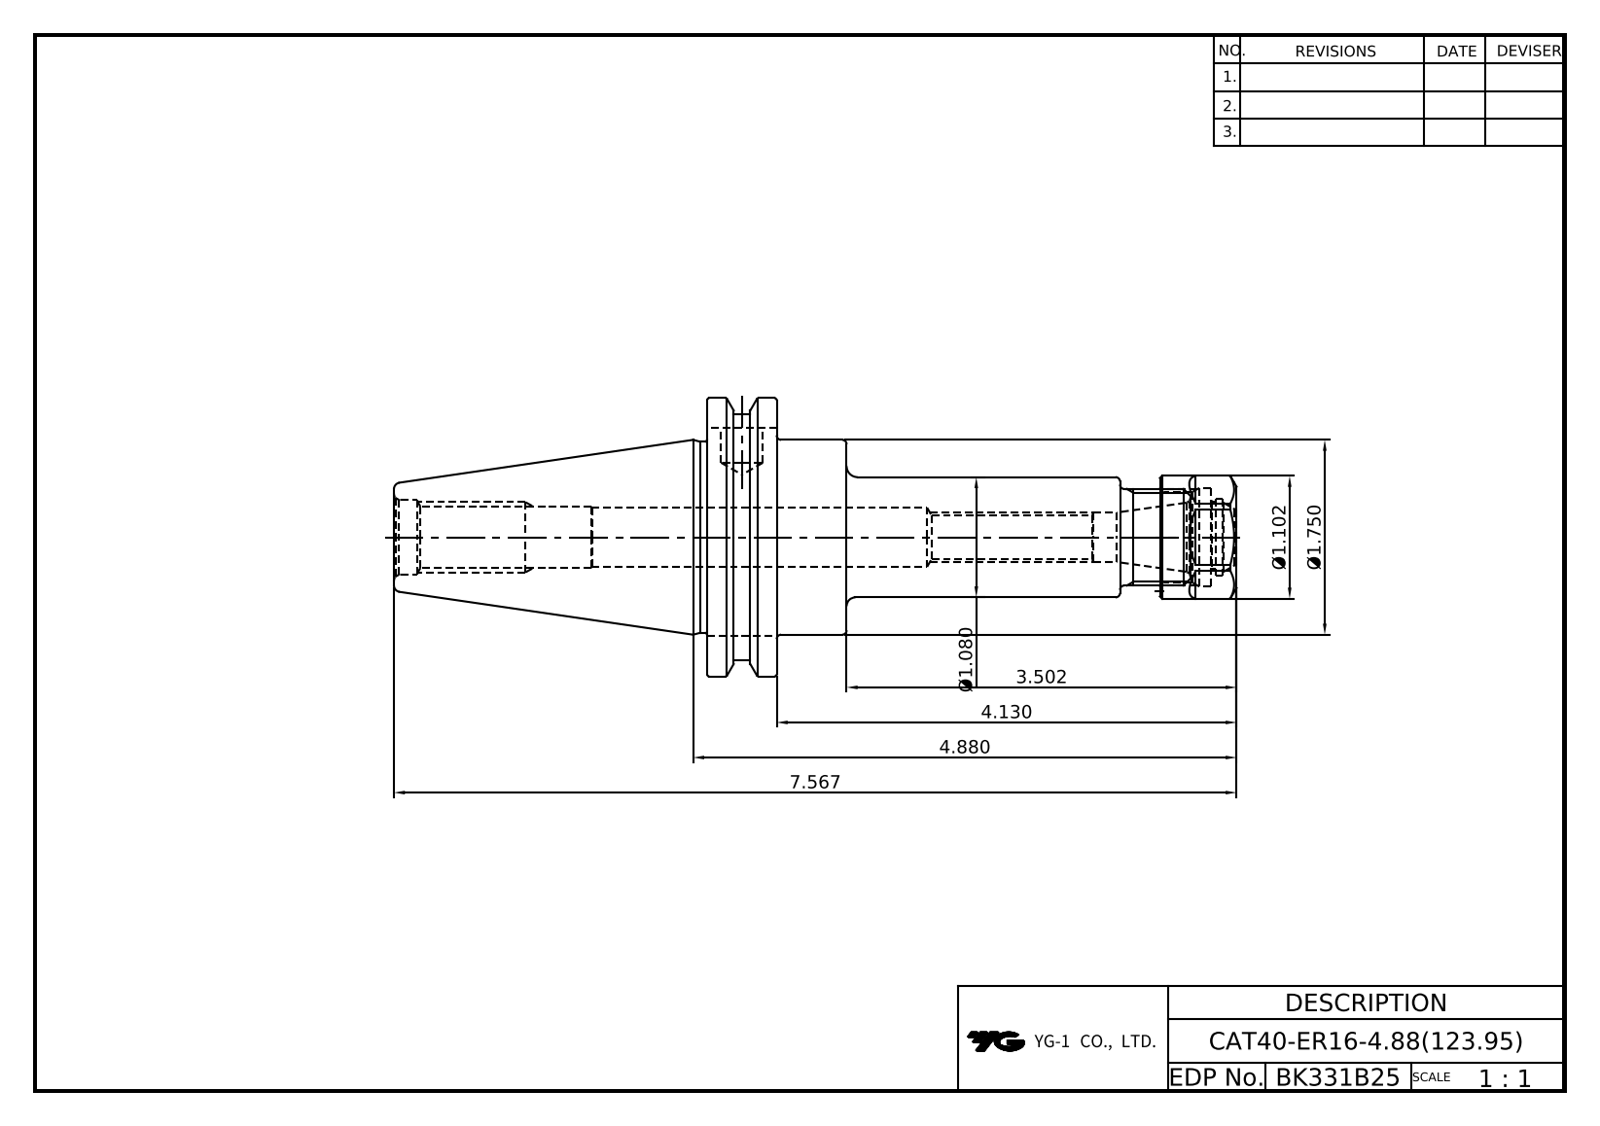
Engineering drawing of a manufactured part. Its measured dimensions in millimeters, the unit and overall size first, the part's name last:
Units: millimetres
Overall size (bounding box): 192.2 × 63.5 × 61.09
Round holes (diameter × count): ⌀1 ×1, ⌀9.4 ×1, ⌀9.53 ×1, ⌀11.3 ×1, ⌀12.8 ×1, ⌀13.39 ×1, ⌀16.3 ×1, ⌀17.7 ×1, ⌀20.6 ×1, ⌀22.5 ×1
Round bosses / shafts (diameter × count): ⌀63.5 ×1, ⌀56.3 ×1, ⌀44.45 ×1, ⌀43.6 ×1, ⌀28 ×1, ⌀22 ×1
Partial cylindrical surfaces — rounded edges, fillets, slot ends (radius × count): R7.7 ×2
Main face-to-face distances: 15.88, 31.83, 15.95, 120.78, 104.9, 88.95, 4.8, 94.18, 78.3, 62.35
Hole centre spacings: 12
Volume: 164 359 mm³ · Surface area: 36 507 mm²
Bodies: 2 solids, 95 faces (49 planar, 24 cylindrical, 22 other)
Part name (STEP PRODUCT): LO-CAT40-ER16-123.95; ER16NUT
STEP written by: Autodesk Inventor 2025 (AUTOMOTIVE_DESIGN)
